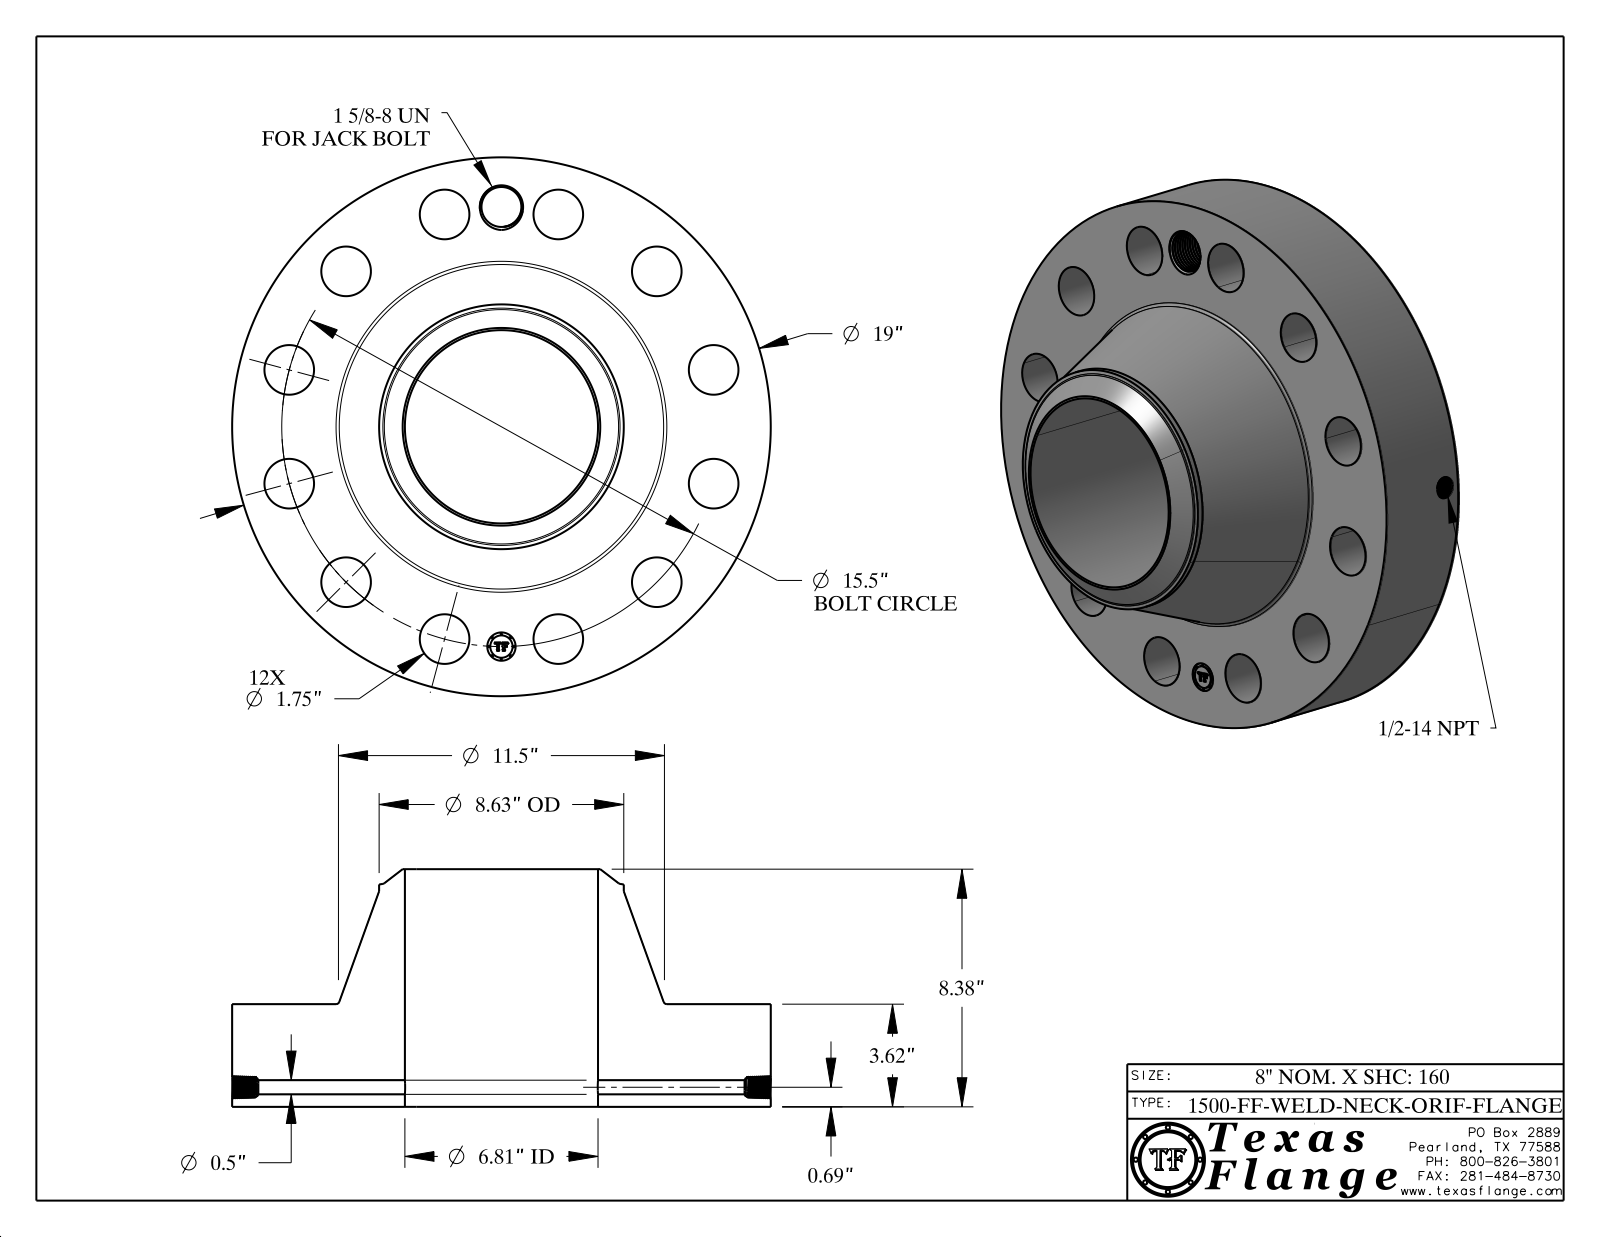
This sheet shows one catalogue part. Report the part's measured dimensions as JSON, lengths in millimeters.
{"part_name": "1500-FF-WELD-NECK", "step_written_by": "CATIA V5 STEP AP214 (AUTOMOTIVE_DESIGN)", "units": "millimeters", "bodies": {"solids": 1, "faces": 862, "planar": 368, "cylindrical": 127, "other": 367}, "overall_size": [482.6, 482.6, 212.9], "volume_mm3": 15820000, "surface_area_mm2": 788400, "round_holes": [[44.5, 12], [12.7, 1], [17.1, 1], [25.4, 1], [35.8, 1], [173.1, 1]], "round_bosses_or_shafts": [[1.5, 8], [482.6, 1], [219.2, 1], [20, 1]], "face_to_face_distances": [91.9, 212.9, 120.9, 91.6, 0.4, 121.3, 7.6, 7.4, 1.4, 6.3], "hole_center_spacings": [196.9, 340.9, 380.3, 101.9, 196.9, 278.4, 393.7, 51.4]}
